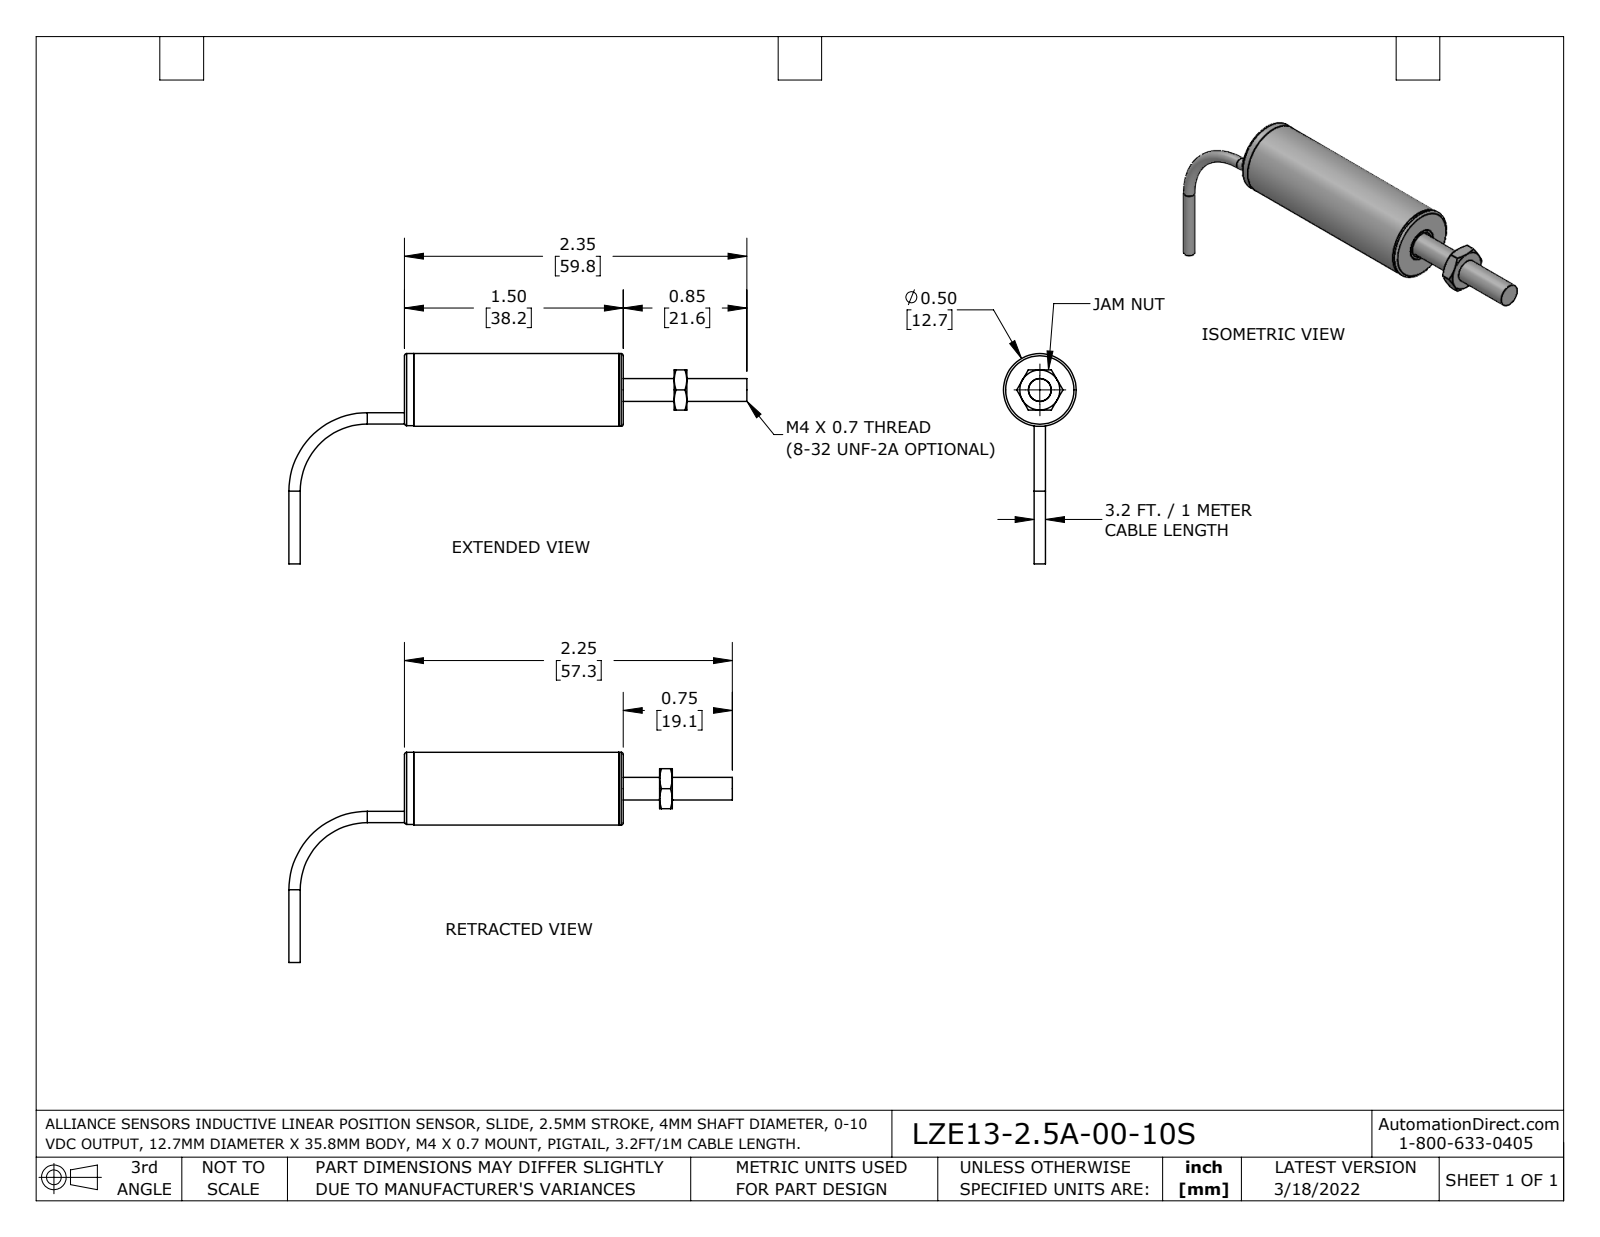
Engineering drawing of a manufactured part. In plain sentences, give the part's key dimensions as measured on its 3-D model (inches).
The part is named "3120-0040_SHRINK; 5500-0029; LZE13-2.5A-00-10S; 3120-0032 (+6 more)". Its 3-D file was written by "SolidWorks 2021 (AUTOMOTIVE_DESIGN)". It is 9 solids with 98 faces: 32 planar, 38 cylindrical and 28 other. Overall it measures 3.149 by 1.445 by 0.5 inches. Its volume is 0.151 cubic inches and its surface area 9.928 square inches. Round holes: 1 of diameter 0.078, 1 of diameter 0.157, 1 of diameter 0.187, 1 of diameter 0.223. Round bosses or shafts: 1 of diameter 0.5, 1 of diameter 0.468, 1 of diameter 0.222, 1 of diameter 0.156, 1 of diameter 0.1, 1 of diameter 0.078. Partial cylindrical surfaces (rounded edges, fillets, slot ends): 1 of radius 0.047. The main face-to-face distances are 0.079, 0.062, 0.276, 0.094, 1.504, 1.442, 1.41, 1.348, 0.031, 0.35. The hole center spacings are 0.195.
